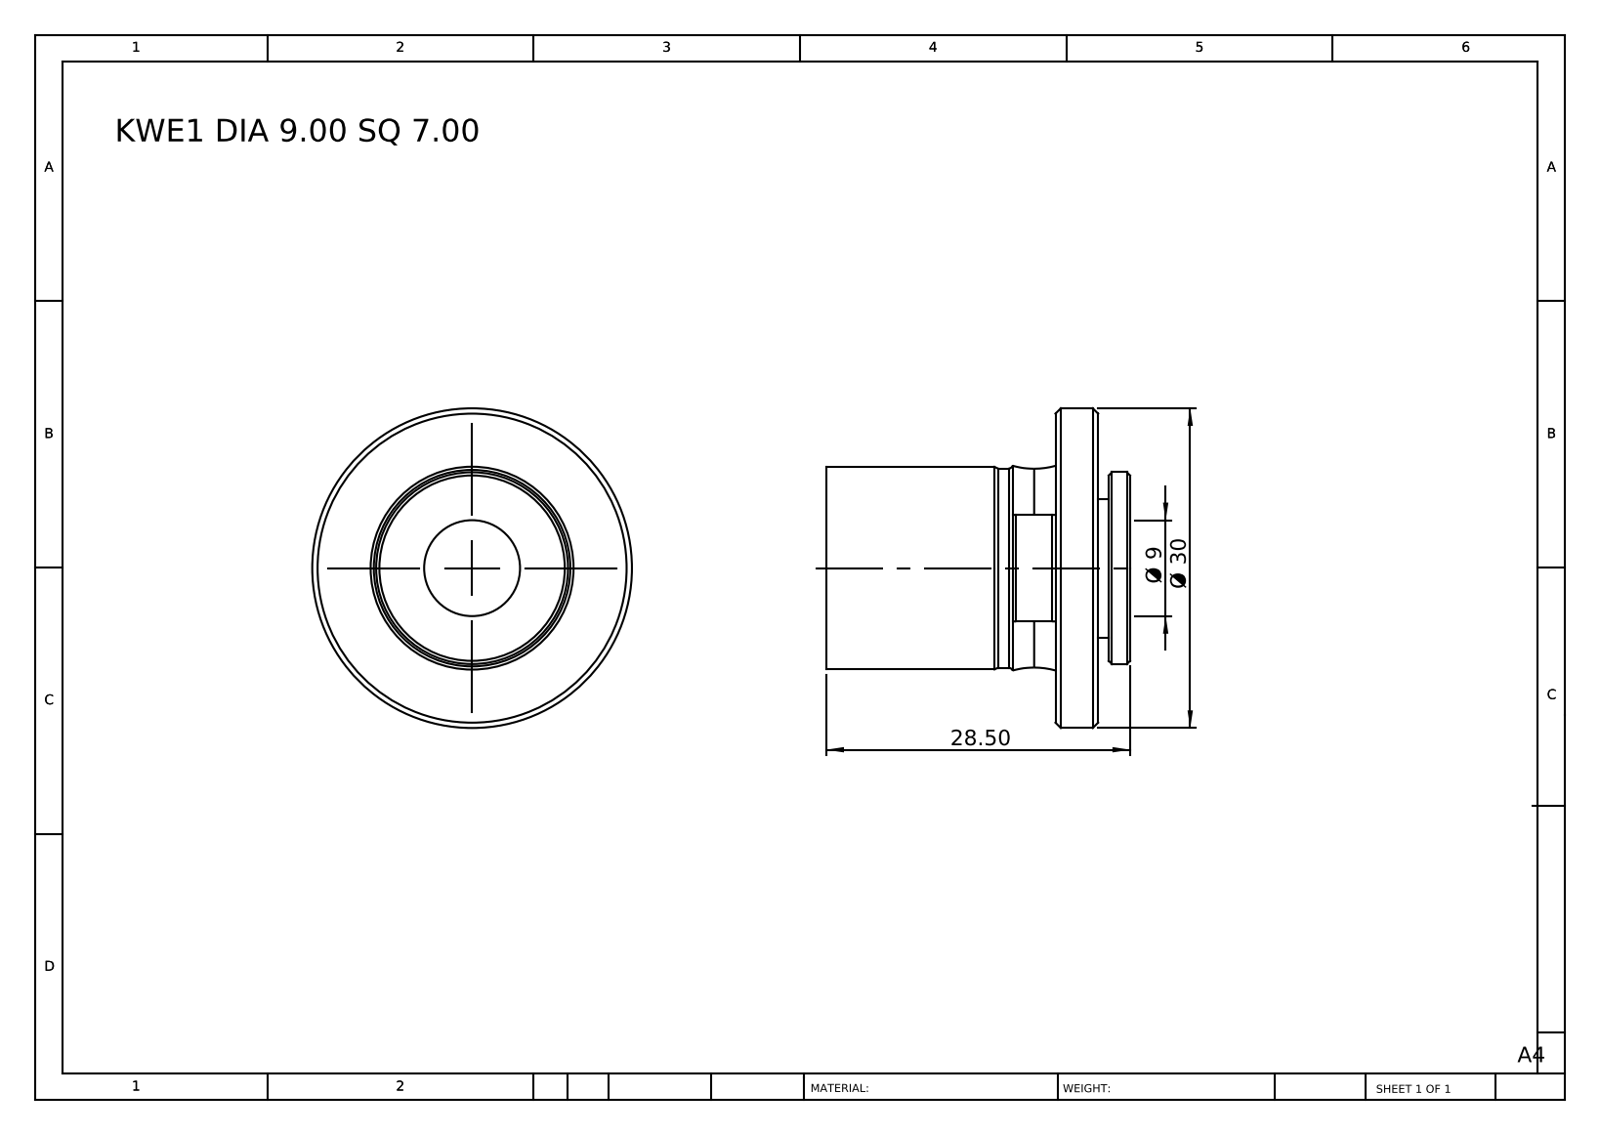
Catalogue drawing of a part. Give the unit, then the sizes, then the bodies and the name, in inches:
Units: inches
Overall size (bounding box): 1.181 × 1.181 × 1.122
Round holes (diameter × count): ⌀0.354 ×1, ⌀0.75 ×1
Round bosses / shafts (diameter × count): ⌀1.181 ×1, ⌀0.748 ×1, ⌀0.736 ×1, ⌀0.709 ×1, ⌀0.512 ×1
Partial cylindrical surfaces — rounded edges, fillets, slot ends (radius × count): R0.488 ×1
Main face-to-face distances: 0.157, 0.846, 1.004, 1.122, 0.276, 0.118, 0.315, 1.043, 0.197, 0.039
Volume: 0.536 in³ · Surface area: 6.008 in²
Bodies: 1 solid, 55 faces (13 planar, 16 cylindrical, 26 other)
Part name (STEP PRODUCT): KWE1 DIA 9.00 SQ 7.00
STEP written by: SolidWorks 2014 (CONFIG_CONTROL_DESIGN)
